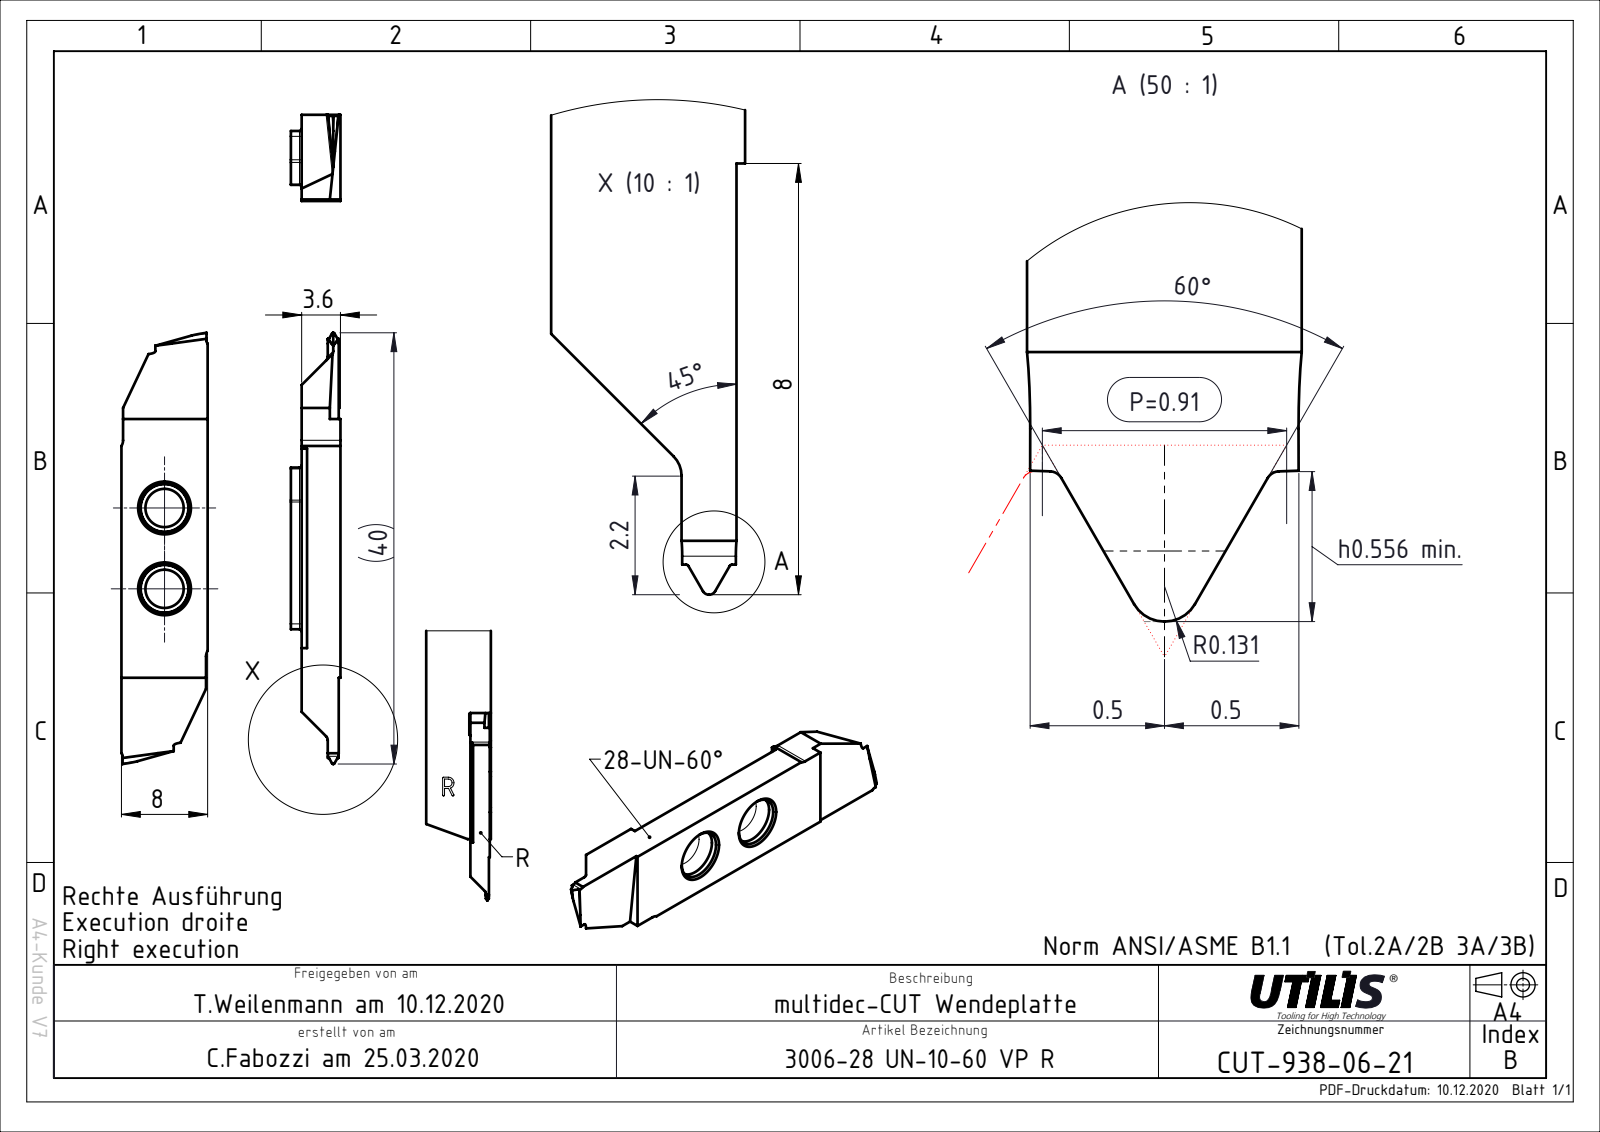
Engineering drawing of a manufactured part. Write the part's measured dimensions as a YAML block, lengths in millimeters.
part_name: "CUT-938-06; ASME Y14.5"
step_written_by: "FormatWorks Professional (AP242_MANAGED_MODEL_BASED_3D_ENGINEERING_MIM_LF)"
units: millimeters
bodies: {solids: 1, faces: 50, planar: 32, cylindrical: 18, other: 0}
overall_size: [40, 8, 3.6]
volume: 864
surface_area: 885
round_holes:
  - {diameter: 3.55, count: 2}
partial_cylinders:
  - {radius: 0.13, count: 4}
  - {radius: 0.5, count: 2}
  - {radius: 1, count: 2}
face_to_face_distances: [3.6, 8, 7.85, 0.86, 18.08, 7.7, 24.94, 4, 4.15, 11.85]
hole_center_spacings: [7.5]
